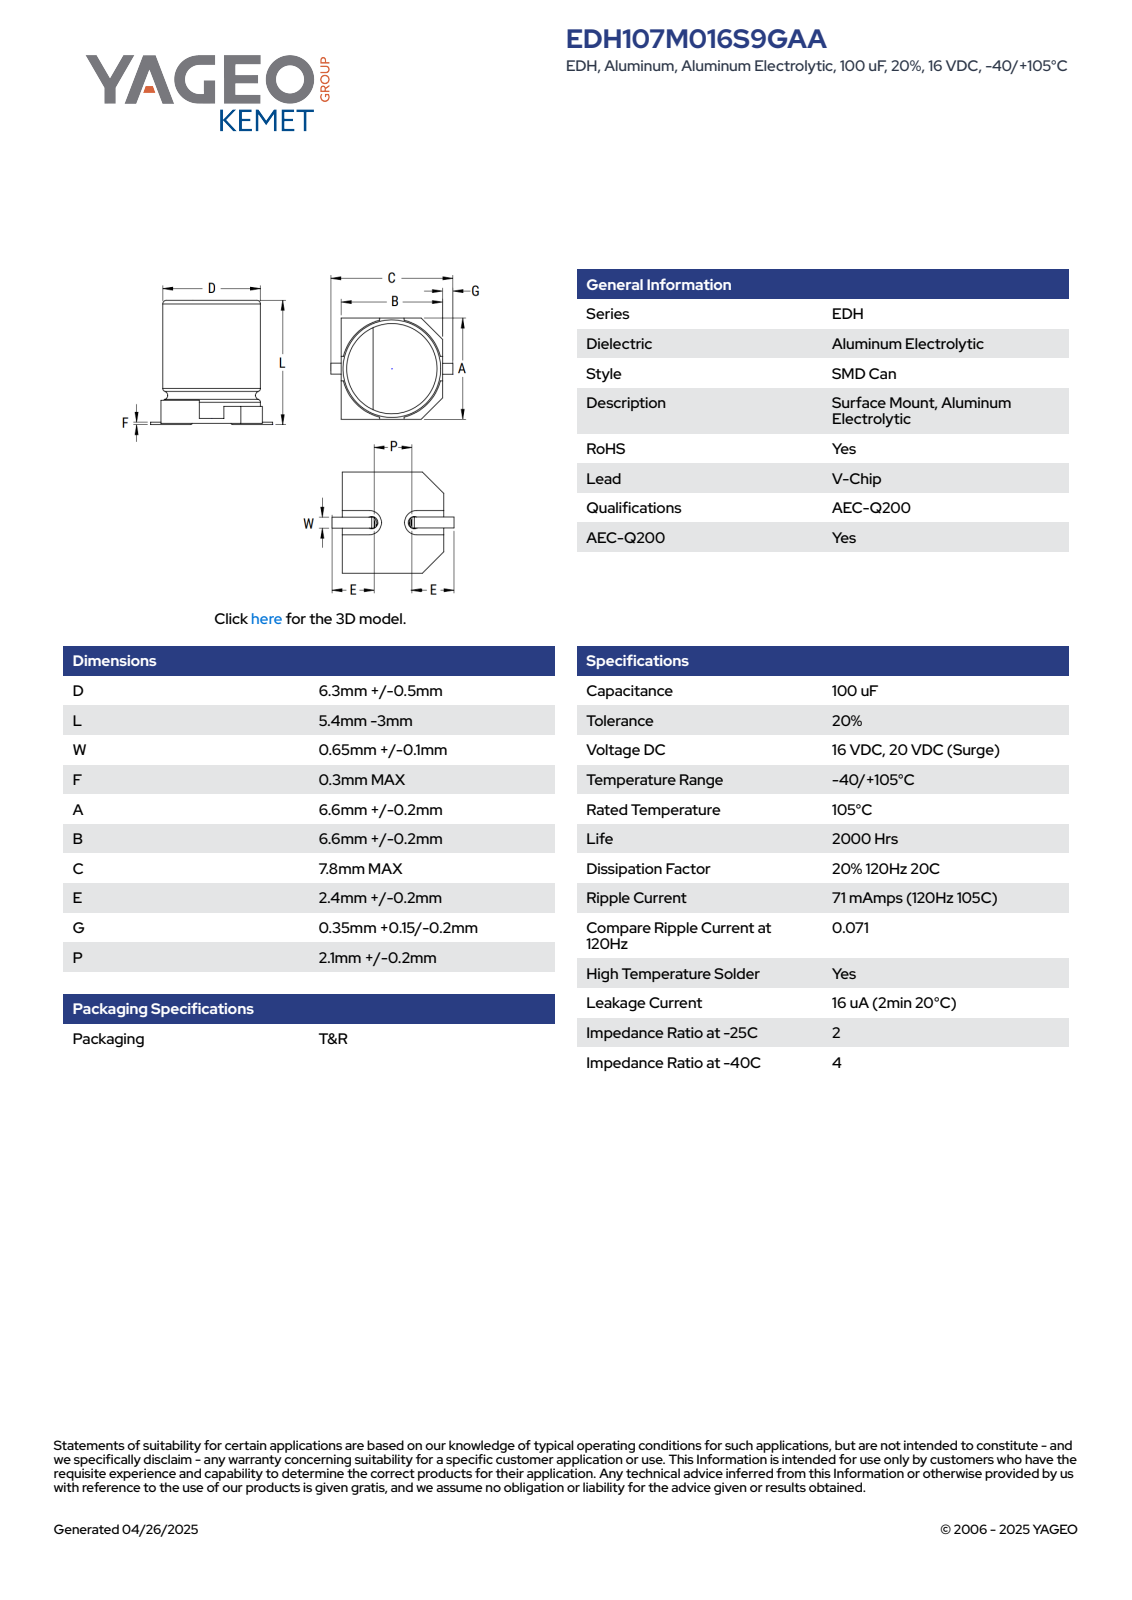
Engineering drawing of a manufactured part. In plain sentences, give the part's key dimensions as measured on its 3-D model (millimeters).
The part is named "CAC_S_6.3X5.4_D6.8L5.65W0.75F0.3A6.8B6.8C7.8E2.8P2". Its 3-D file was written by "SolidWorks 2014 (AUTOMOTIVE_DESIGN)". It is 5 solids with 78 faces: 61 planar, 11 cylindrical and 6 other. Overall it measures 7.6 by 6.8 by 5.66 millimeters. Its volume is 186 cubic millimeters and its surface area 300 square millimeters. Round bosses or shafts: 1 of diameter 6.5. Partial cylindrical surfaces (rounded edges, fillets, slot ends): 2 of radius 0.2, 1 of radius 2.7, 1 of radius 3.4. The main face-to-face distances are 5.35, 5.07, 5.36, 5.08, 6.8, 1.13, 1.41, 3.94, 3.95, 0.58.
